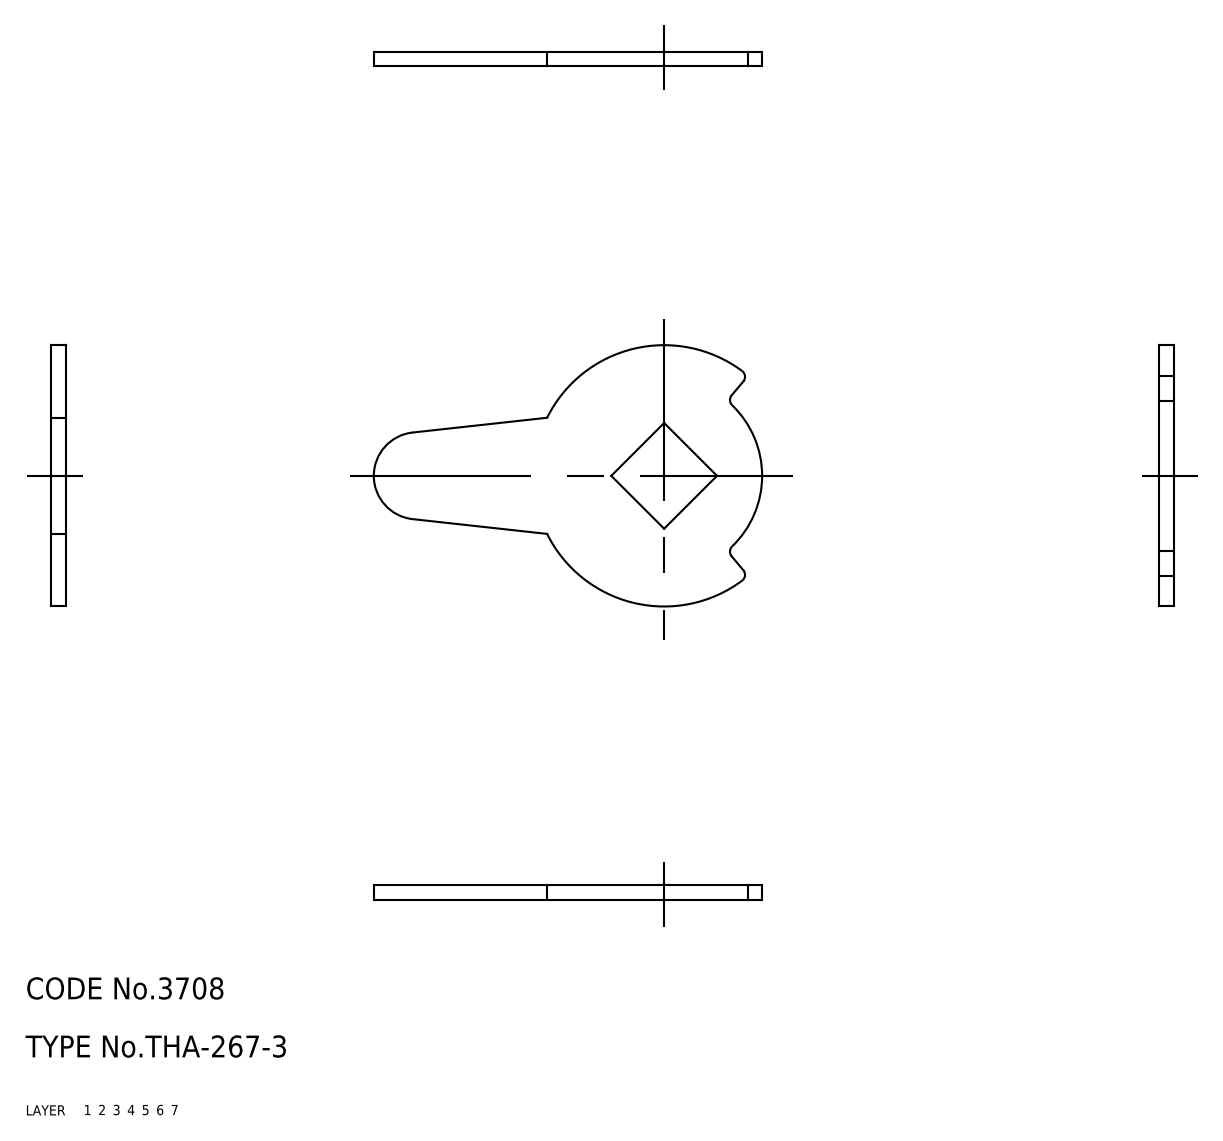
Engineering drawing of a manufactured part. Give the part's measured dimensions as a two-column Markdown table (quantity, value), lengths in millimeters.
| quantity | value |
| --- | --- |
| part name | cam |
| STEP written by | CADfix (AUTOMOTIVE_DESIGN) |
| units | millimeters |
| bodies | 1 solid, 18 faces (0 planar, 0 cylindrical, 18 other) |
| overall size | 53.5 × 36 × 2 |
| volume | 2 151 mm³ |
| surface area | 2 534 mm² |
